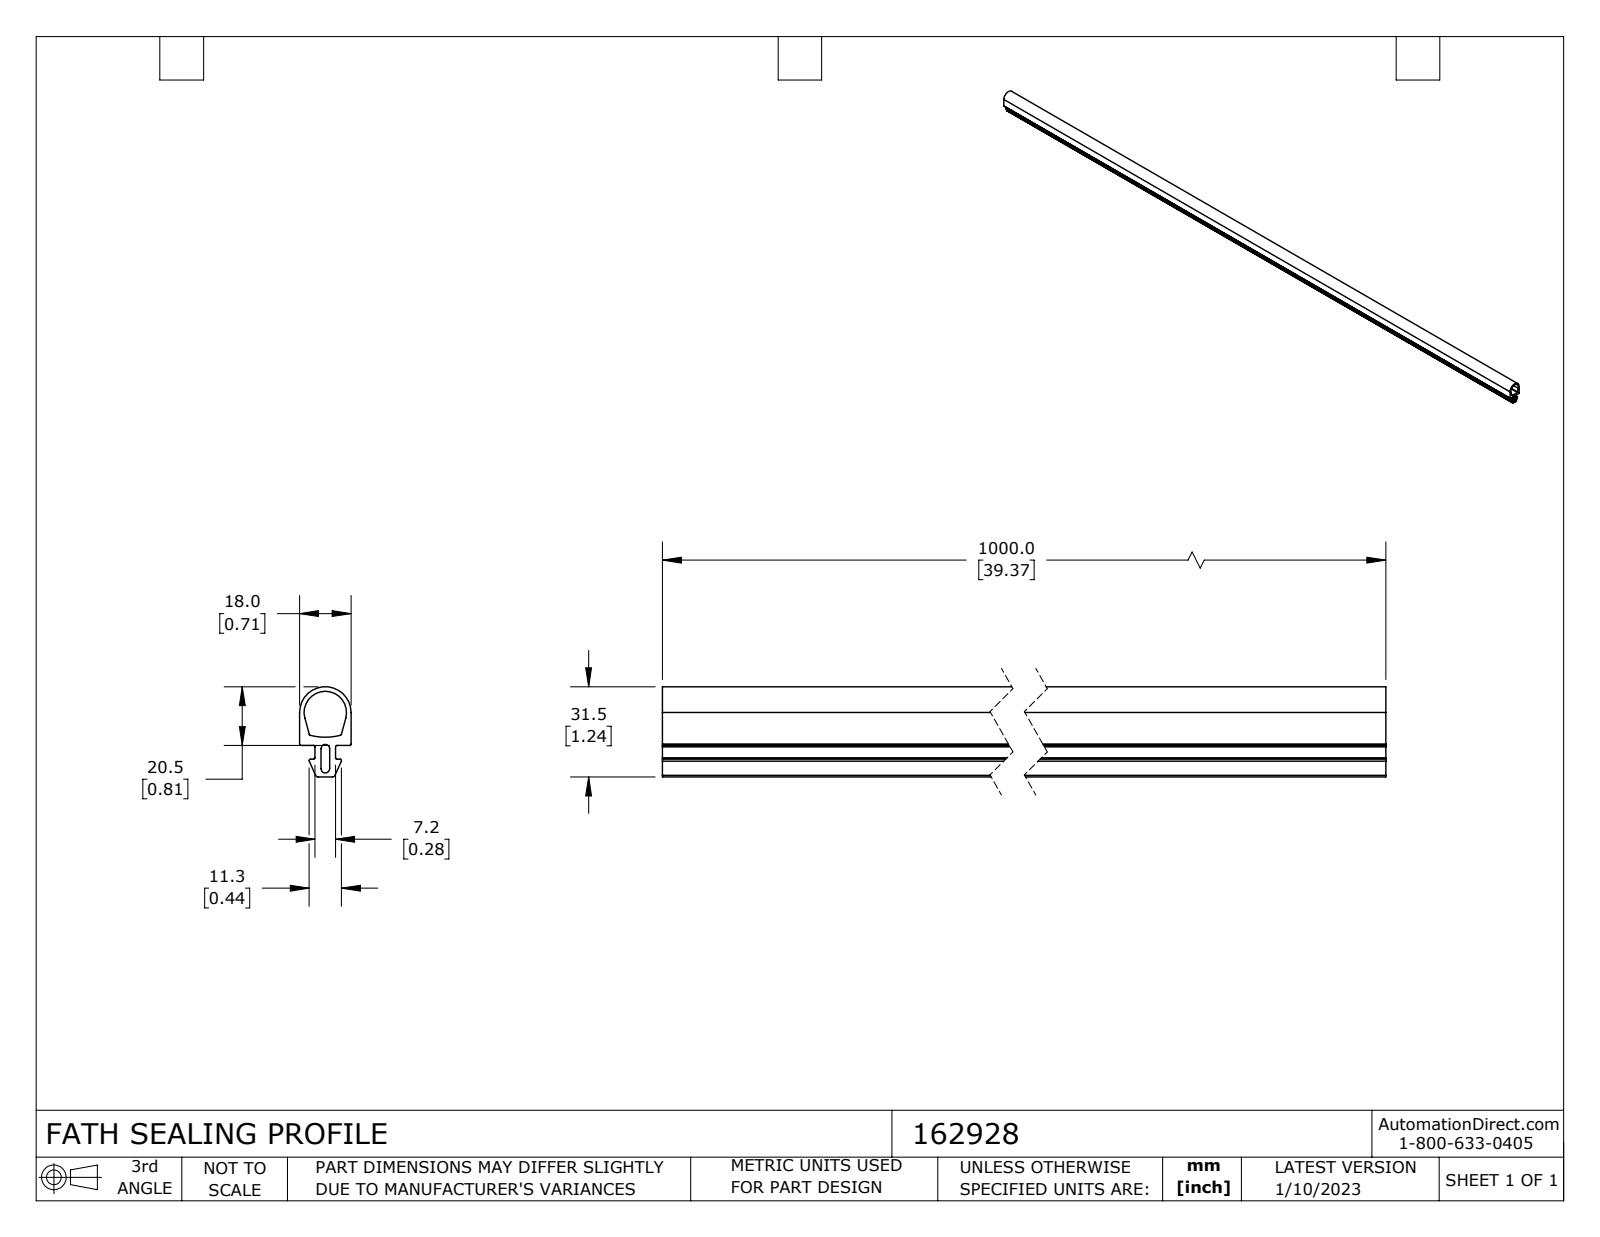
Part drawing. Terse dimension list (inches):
name: 162928
written by: SolidWorks 2021 (CONFIG_CONTROL_DESIGN)
unit: in
bodies: 1 solid, 37 faces (17 planar, 20 cylindrical, 0 other)
size: 39.37 × 1.24 × 0.709
volume: 12.29 in³; area: 260.3 in²
rounds: 10× R0.02, 2× R0.039, 2× R0.059, 1× R0.291, 1× R0.354, 1× R0.866
face distances: 0.295, 0.413, 0.709, 0.213, 0.496, 0.083, 0.201, 0.118, 0.433, 0.283
